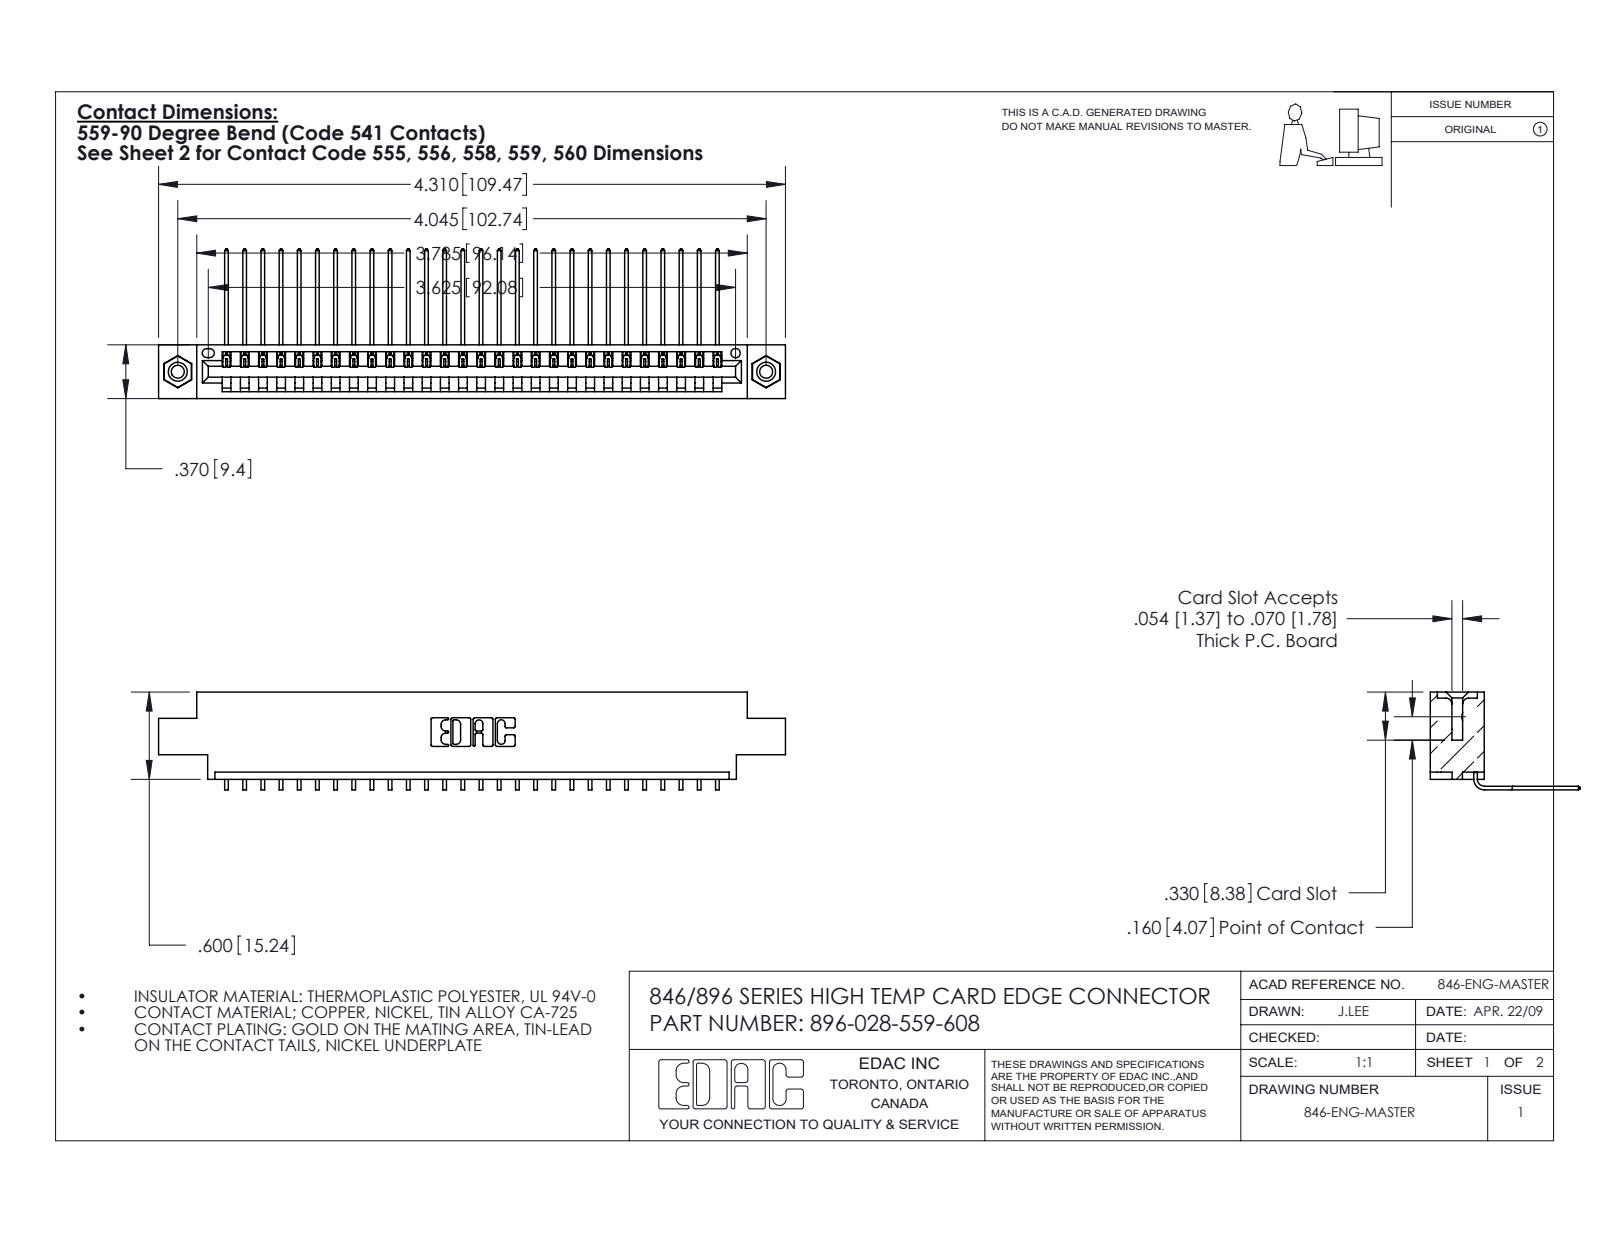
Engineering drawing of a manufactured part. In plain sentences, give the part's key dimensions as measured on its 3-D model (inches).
The part is named "396-028-559-608; 345-292-001_558 559 Tail - 1; 345-250-001_345-250-003-102; 346 Part_0.170 Offset - 0.156 Dia-TI". Its 3-D file was written by "SolidWorks 2016 (CONFIG_CONTROL_DESIGN)". It is 31 solids with 1866 faces: 1288 planar, 562 cylindrical and 16 other. Overall it measures 4.31 by 1.03 by 0.673 inches. Its volume is 0.629 cubic inches and its surface area 20.89 square inches. Round holes: 2 of diameter 0.089, 2 of diameter 0.125, 2 of diameter 0.156, 1 of diameter 0.064. Round bosses or shafts: 2 of diameter 0.155. Partial cylindrical surfaces (rounded edges, fillets, slot ends): 56 of radius 0.006, 22 of radius 0.01, 6 of radius 0.007, 6 of radius 0.031, 3 of radius 0.026, 2 of radius 0.031, 2 of radius 0.04, 1 of radius 0.014. The main face-to-face distances are 0.048, 0.322, 0.37, 0.25, 0.025, 0.072, 0.222, 0.148, 0.1, 0.174. The hole center spacings are 0.246, 3.837, 4.045.
